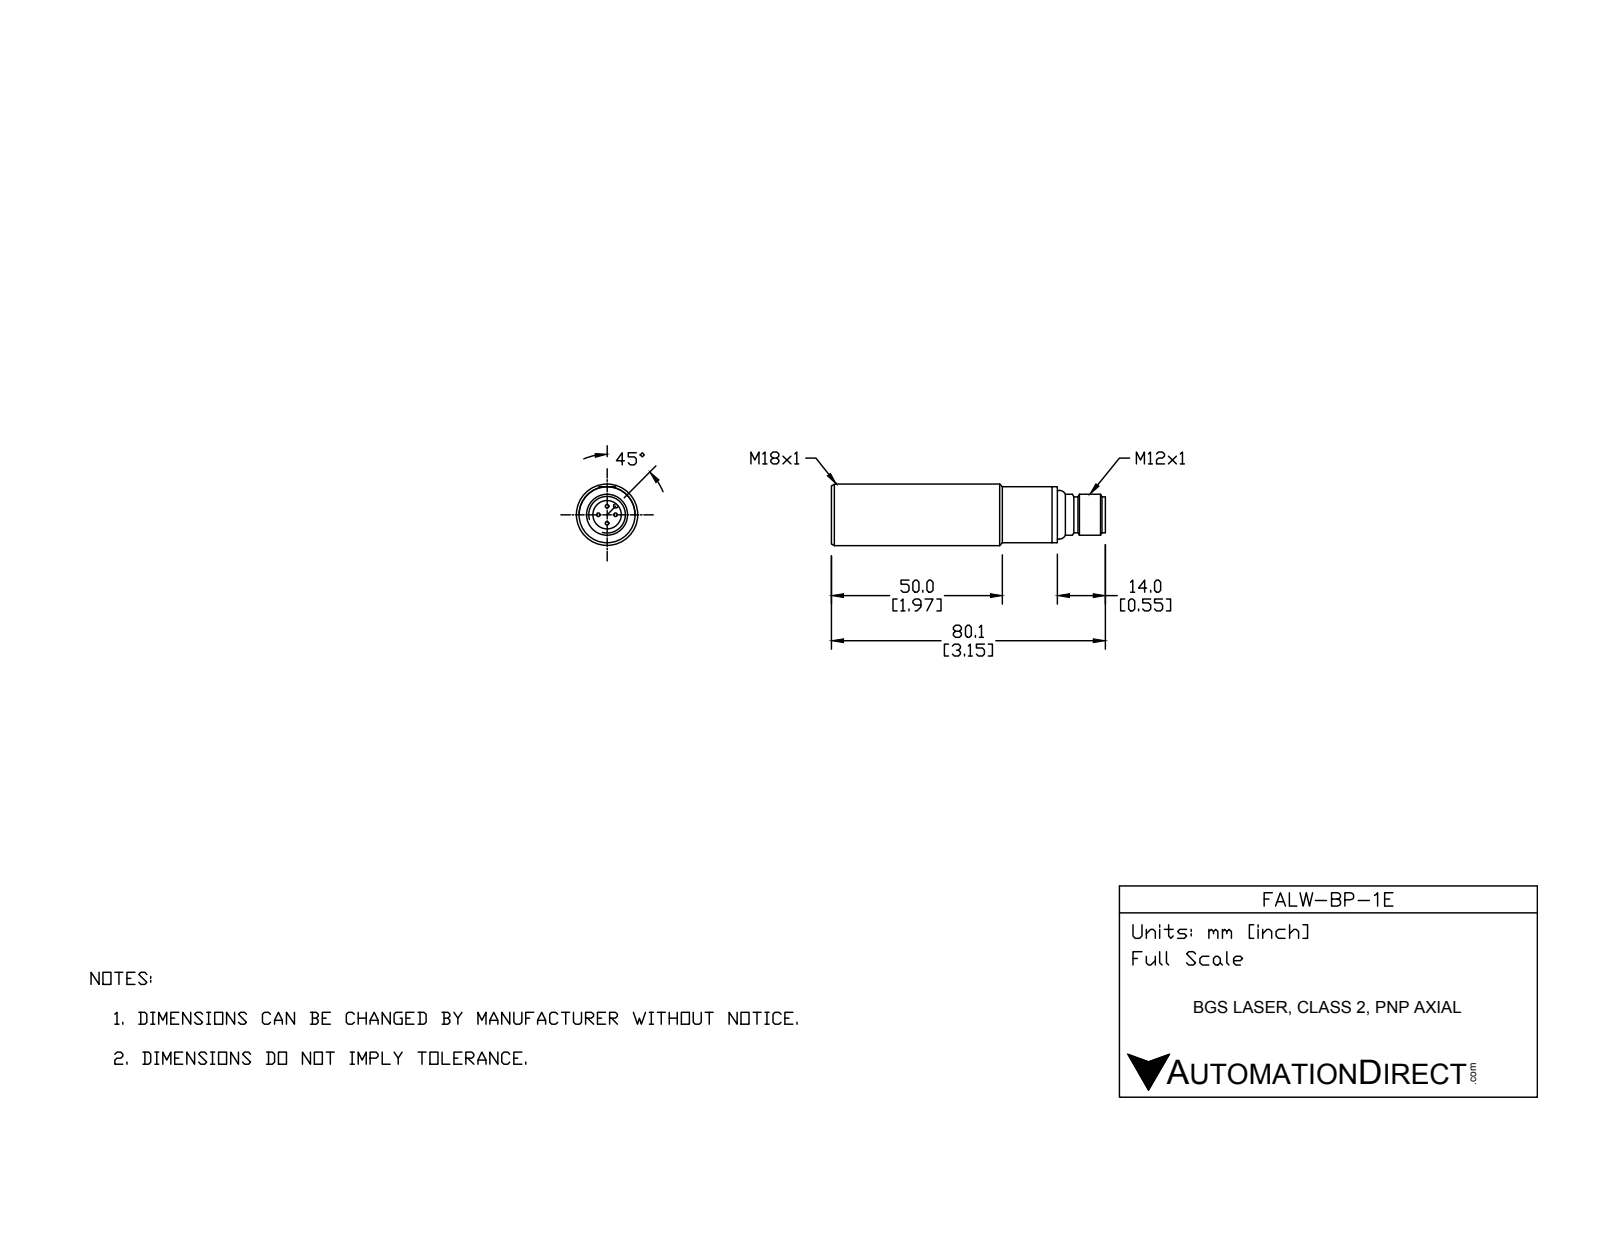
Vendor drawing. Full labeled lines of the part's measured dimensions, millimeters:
Part name (STEP PRODUCT): FALW-BP-1E
STEP written by: SolidWorks 2017 (AUTOMOTIVE_DESIGN)
Units: millimetres
Bodies: 10 solids, 166 faces (50 planar, 73 cylindrical, 43 other)
Overall size (bounding box): 80.1 × 18 × 18
Volume: 17 030 mm³ · Surface area: 6 510 mm²
Round holes (diameter × count): ⌀1 ×4, ⌀1.1 ×4, ⌀2.7 ×1, ⌀4.7 ×1, ⌀7.1 ×1, ⌀8.3 ×1, ⌀15.8 ×1
Round bosses / shafts (diameter × count): ⌀18 ×1, ⌀16.4 ×1, ⌀14.2 ×1, ⌀12 ×1, ⌀10.5 ×1, ⌀7 ×1, ⌀4.8 ×1
Partial cylindrical surfaces — rounded edges, fillets, slot ends (radius × count): R0.5 ×4, R0.6 ×1, R8.4 ×1
Main face-to-face distances: 1.6, 64.3, 1.4, 62.9, 62.7, 64.5, 65.9, 71, 69.6, 69.4
Hole centre spacings: 2.5, 3.5, 5
